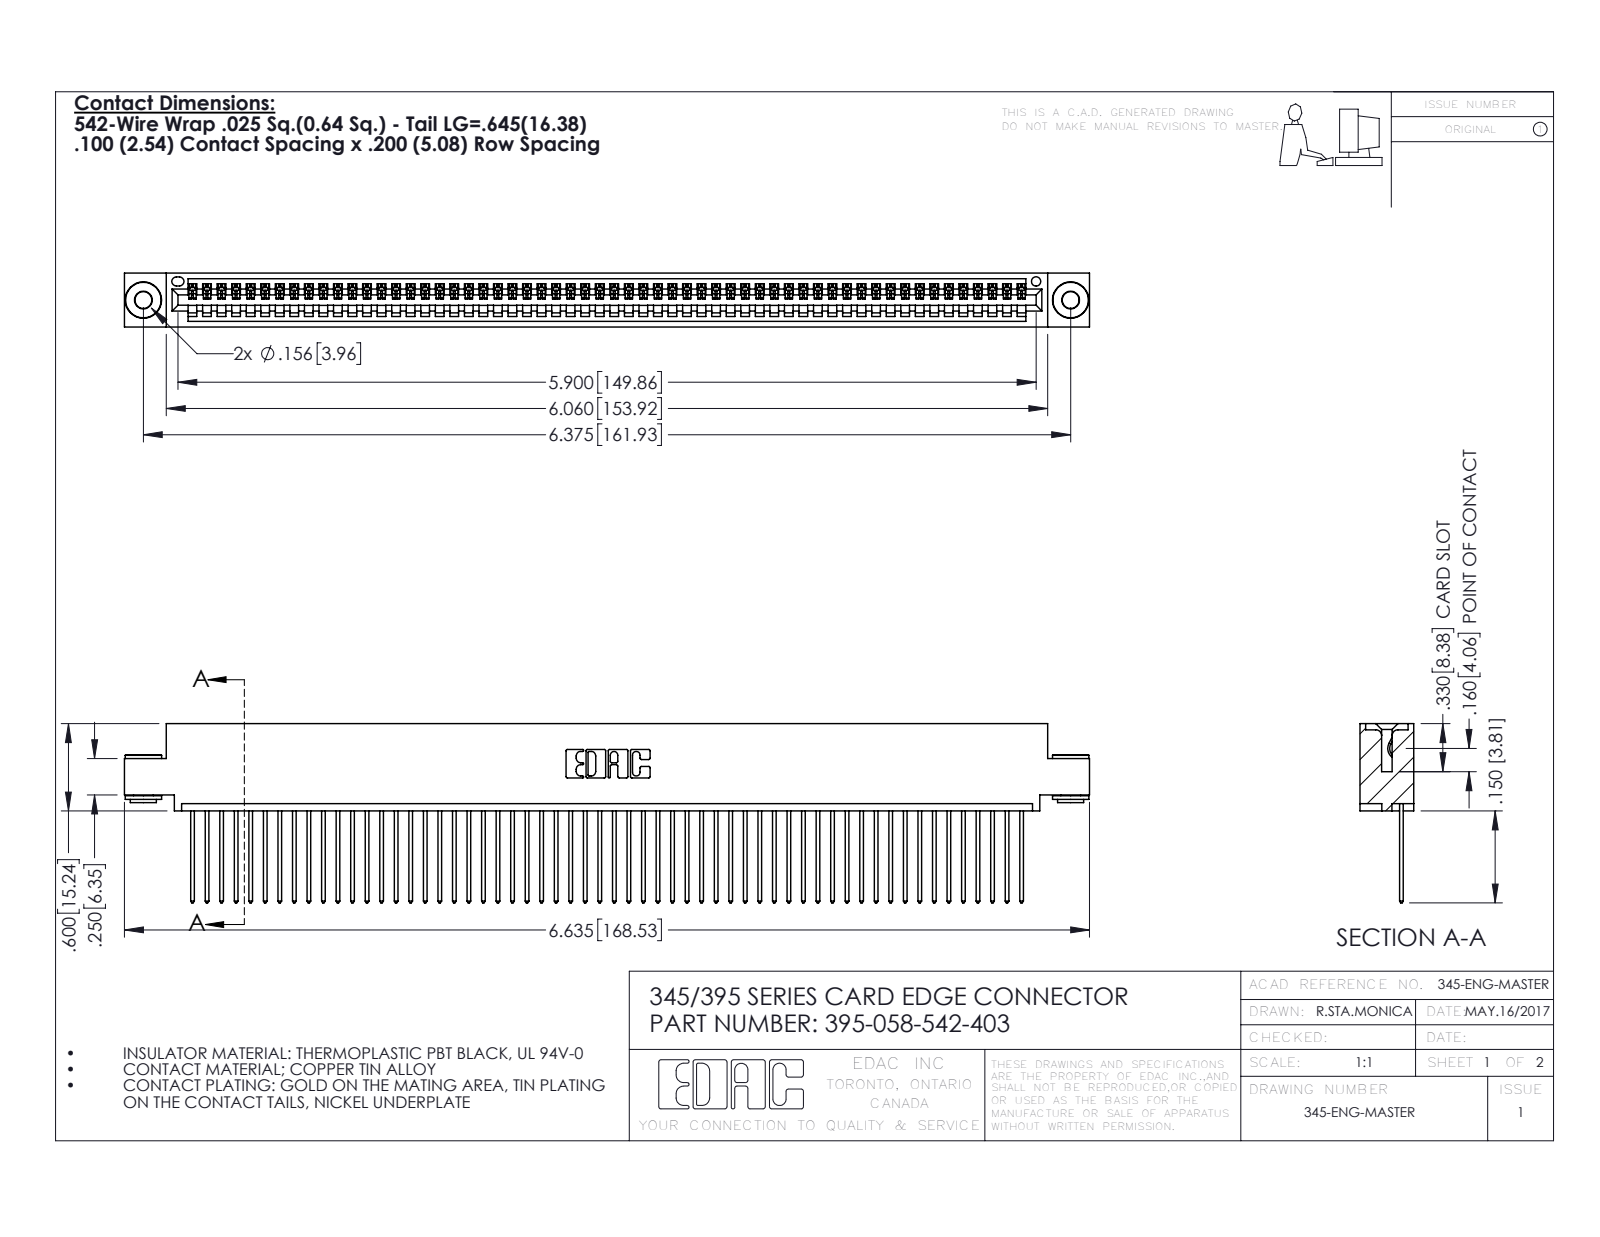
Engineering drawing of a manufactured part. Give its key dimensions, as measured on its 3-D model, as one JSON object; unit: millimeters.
{"part_name": "395-058-542-403; 345-292-001_345-293-142; 345-250-002_345-250-002-102; 345 Part_0.110 Offset - 0.156 Dia-TH", "step_written_by": "SolidWorks 2016 (CONFIG_CONTROL_DESIGN)", "units": "millimeters", "bodies": {"solids": 61, "faces": 3532, "planar": 2414, "cylindrical": 1110, "other": 8}, "overall_size": [168.5, 31.3, 9.4], "volume_mm3": 16200, "surface_area_mm2": 22880, "round_holes": [[2.9, 2], [4, 2], [1.6, 1]], "round_bosses_or_shafts": [[6.4, 2], [4.6, 2], [3.5, 2]], "partial_cylinders_radius": [[0.2, 116], [0.3, 116], [0.3, 22], [0.2, 6], [0.8, 6], [0.7, 3], [0.8, 2], [1, 2]], "face_to_face_distances": [1.8, 7.6, 0.6, 2.5, 6.9, 9.4, 5.1, 5.7, 3.8, 1.8], "hole_center_spacings": [6.9, 155.9, 161.9]}
